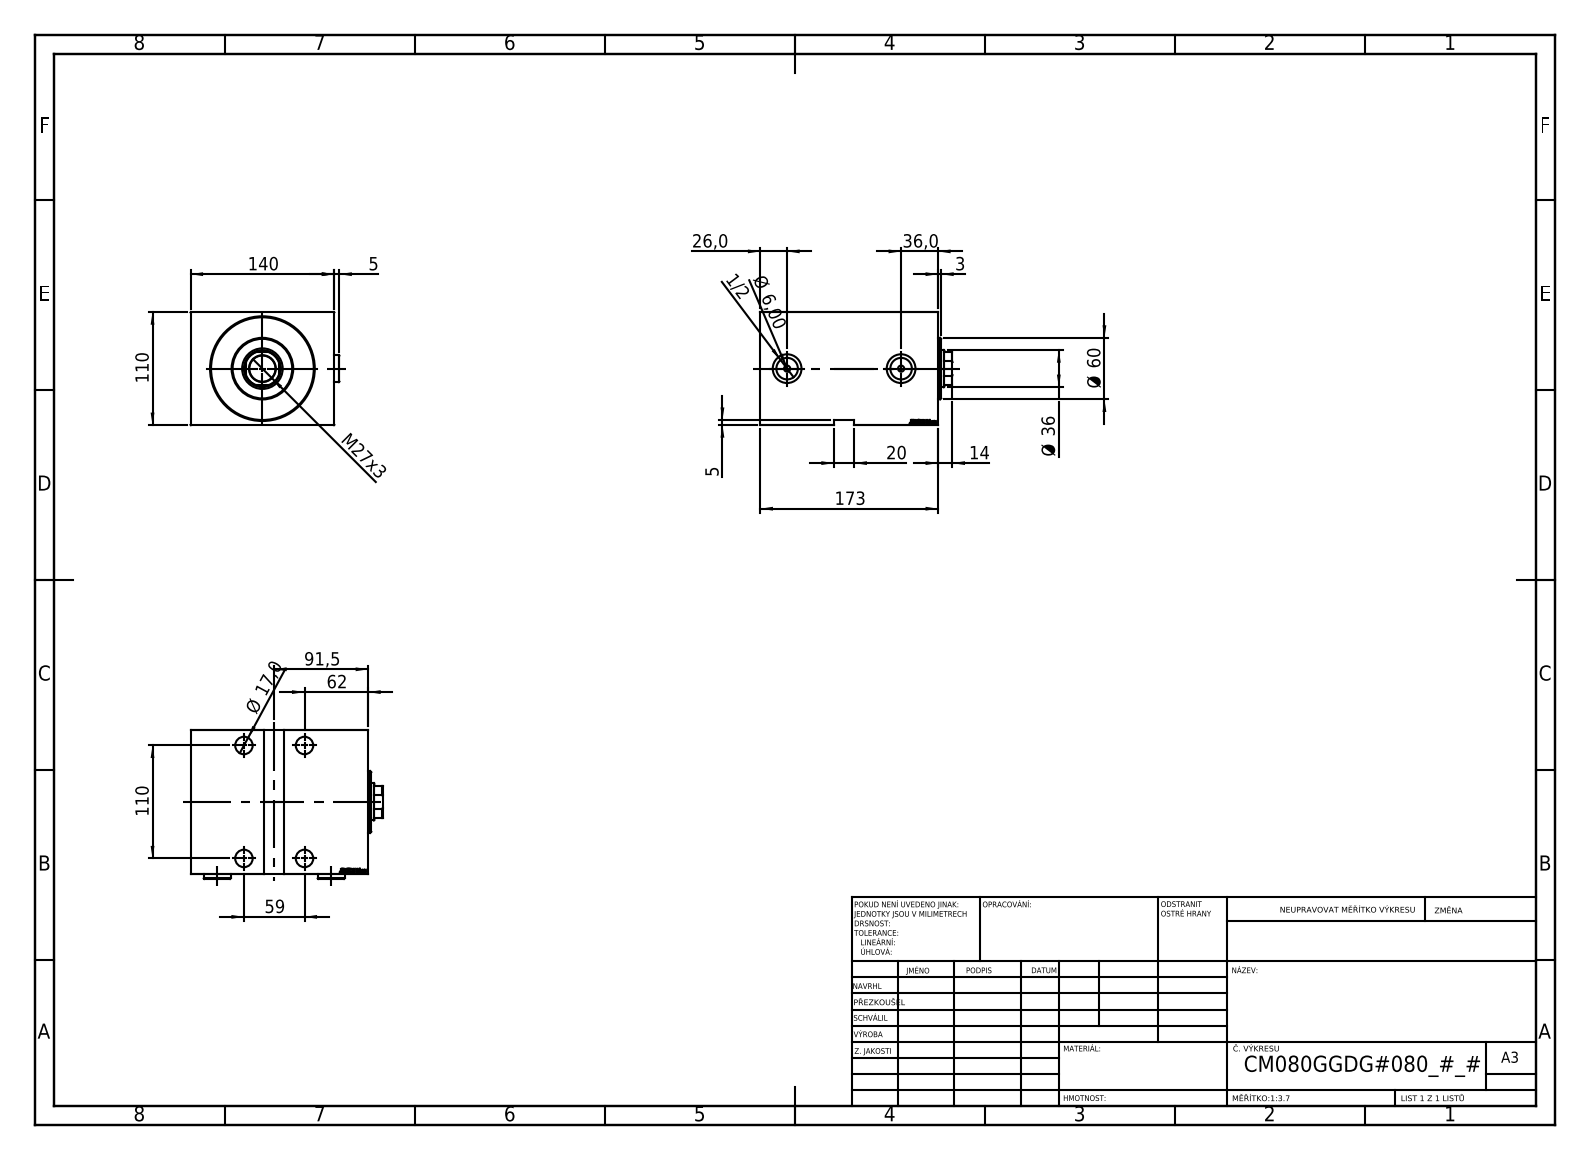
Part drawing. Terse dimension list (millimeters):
name: V450CM_G_VCP; Zatka_OIL_PORT; V450CM_VC_G; V450CM_G_Body
written by: SolidWorks 2019 (CONFIG_CONTROL_DESIGN)
unit: mm
bodies: 5 solids, 912 faces (446 planar, 68 cylindrical, 398 other)
size: 187 × 144.9 × 110
volume: 2 150 000 mm³; area: 244 561 mm²
holes: 4× ⌀17, 4× ⌀25, 2× ⌀6, 2× ⌀20.96, 2× ⌀28, 1× ⌀25.5, 1× ⌀36, 1× ⌀39.5, 1× ⌀80, 1× ⌀82, 1× ⌀100
bosses: 2× ⌀26, 1× ⌀60
rounds: 1× R17.5
face distances: 110, 140, 5, 173, 21, 152, 168, 147, 79, 58
hole spacings: 59, 110, 124.82, 111
